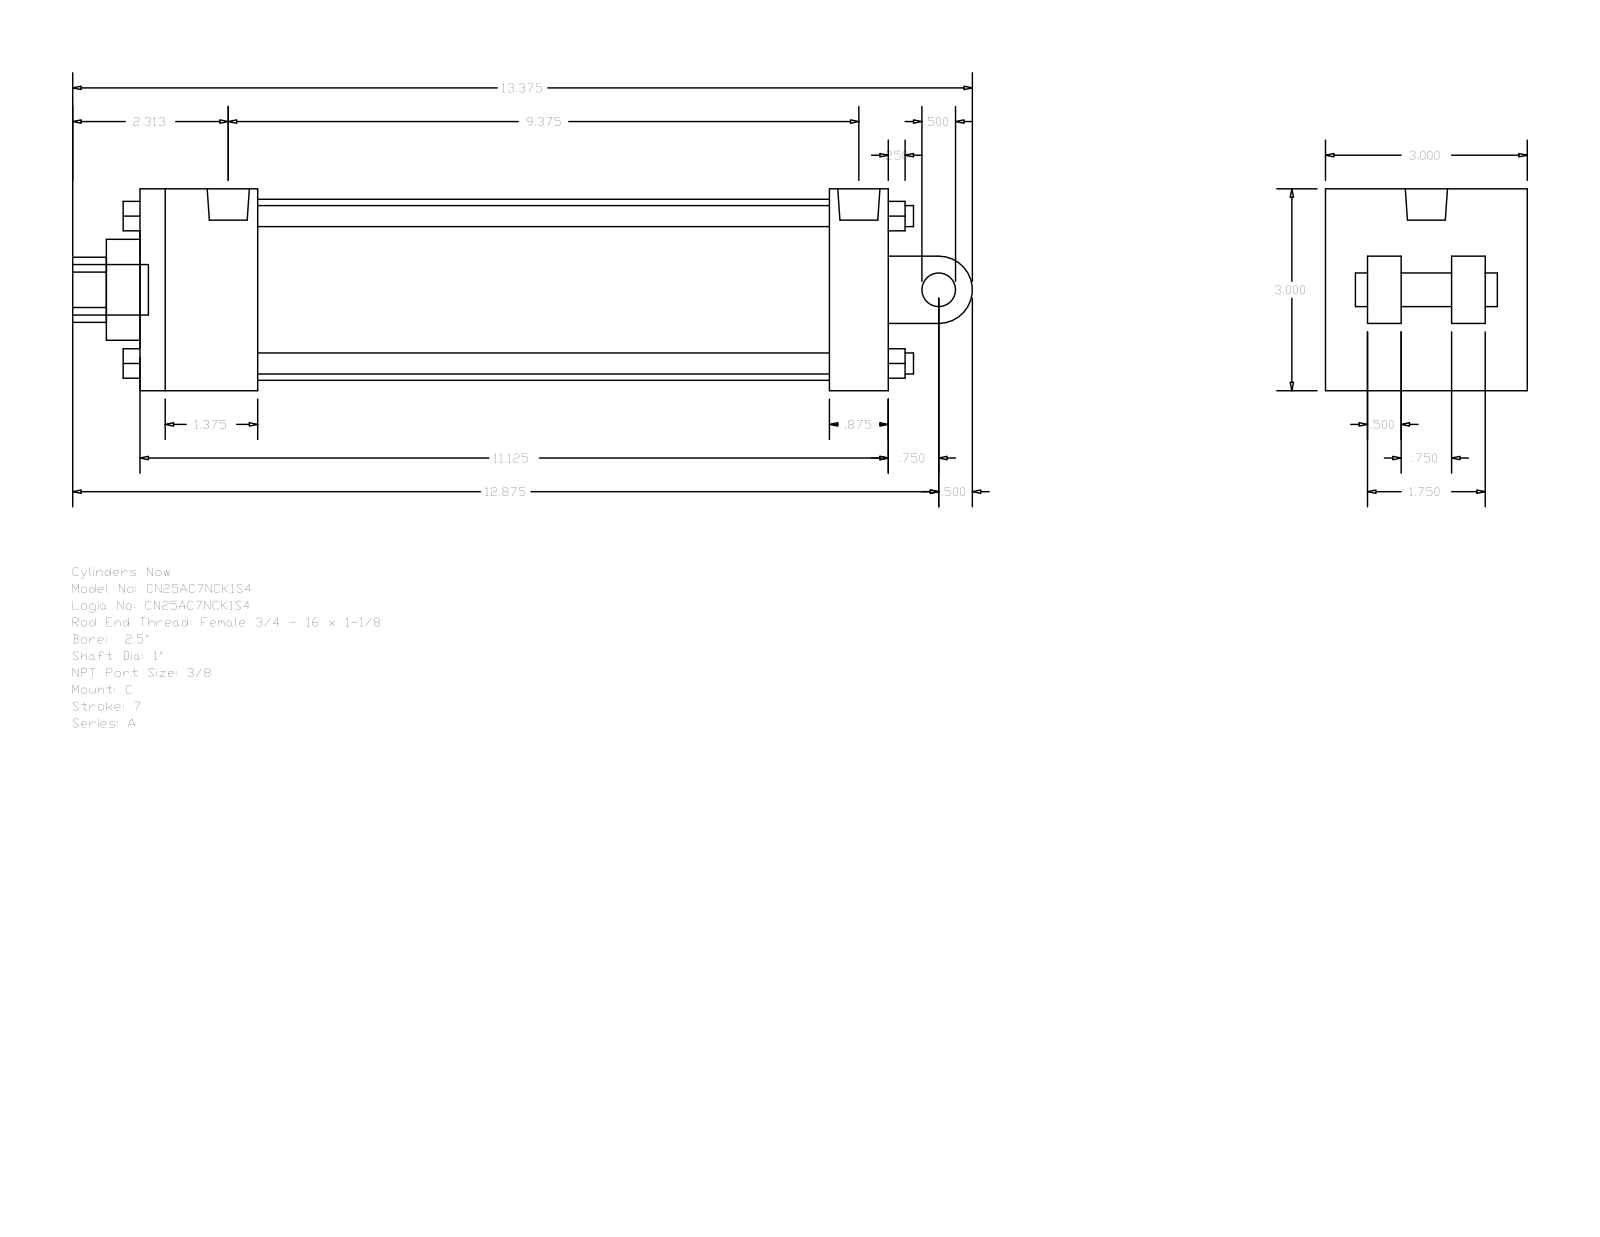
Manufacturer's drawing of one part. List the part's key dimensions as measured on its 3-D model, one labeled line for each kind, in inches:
Part name (STEP PRODUCT): A_C__0250_1
STEP written by: GSSL Pune (CONFIG_CONTROL_DESIGN)
Units: inches
Bodies: 0 solids, 135 faces (102 planar, 33 cylindrical, 0 other)
Overall size (bounding box): 13.375 × 3 × 3
Round holes (diameter × count): ⌀0.219 ×2, ⌀0.627 ×1, ⌀1 ×1, ⌀1.5 ×1, ⌀2.69 ×1
Round bosses / shafts (diameter × count): ⌀0.313 ×4, ⌀0.219 ×2, ⌀0.75 ×1, ⌀0.627 ×1, ⌀0.5 ×1
Partial cylindrical surfaces — rounded edges, fillets, slot ends (radius × count): R0.484 ×1, R0.5 ×1
Main face-to-face distances: 3, 11.125, 0.5, 1.75, 10.25, 8.5, 9.375, 0.875, 0.625, 1
Hole centre spacings: 0.094
